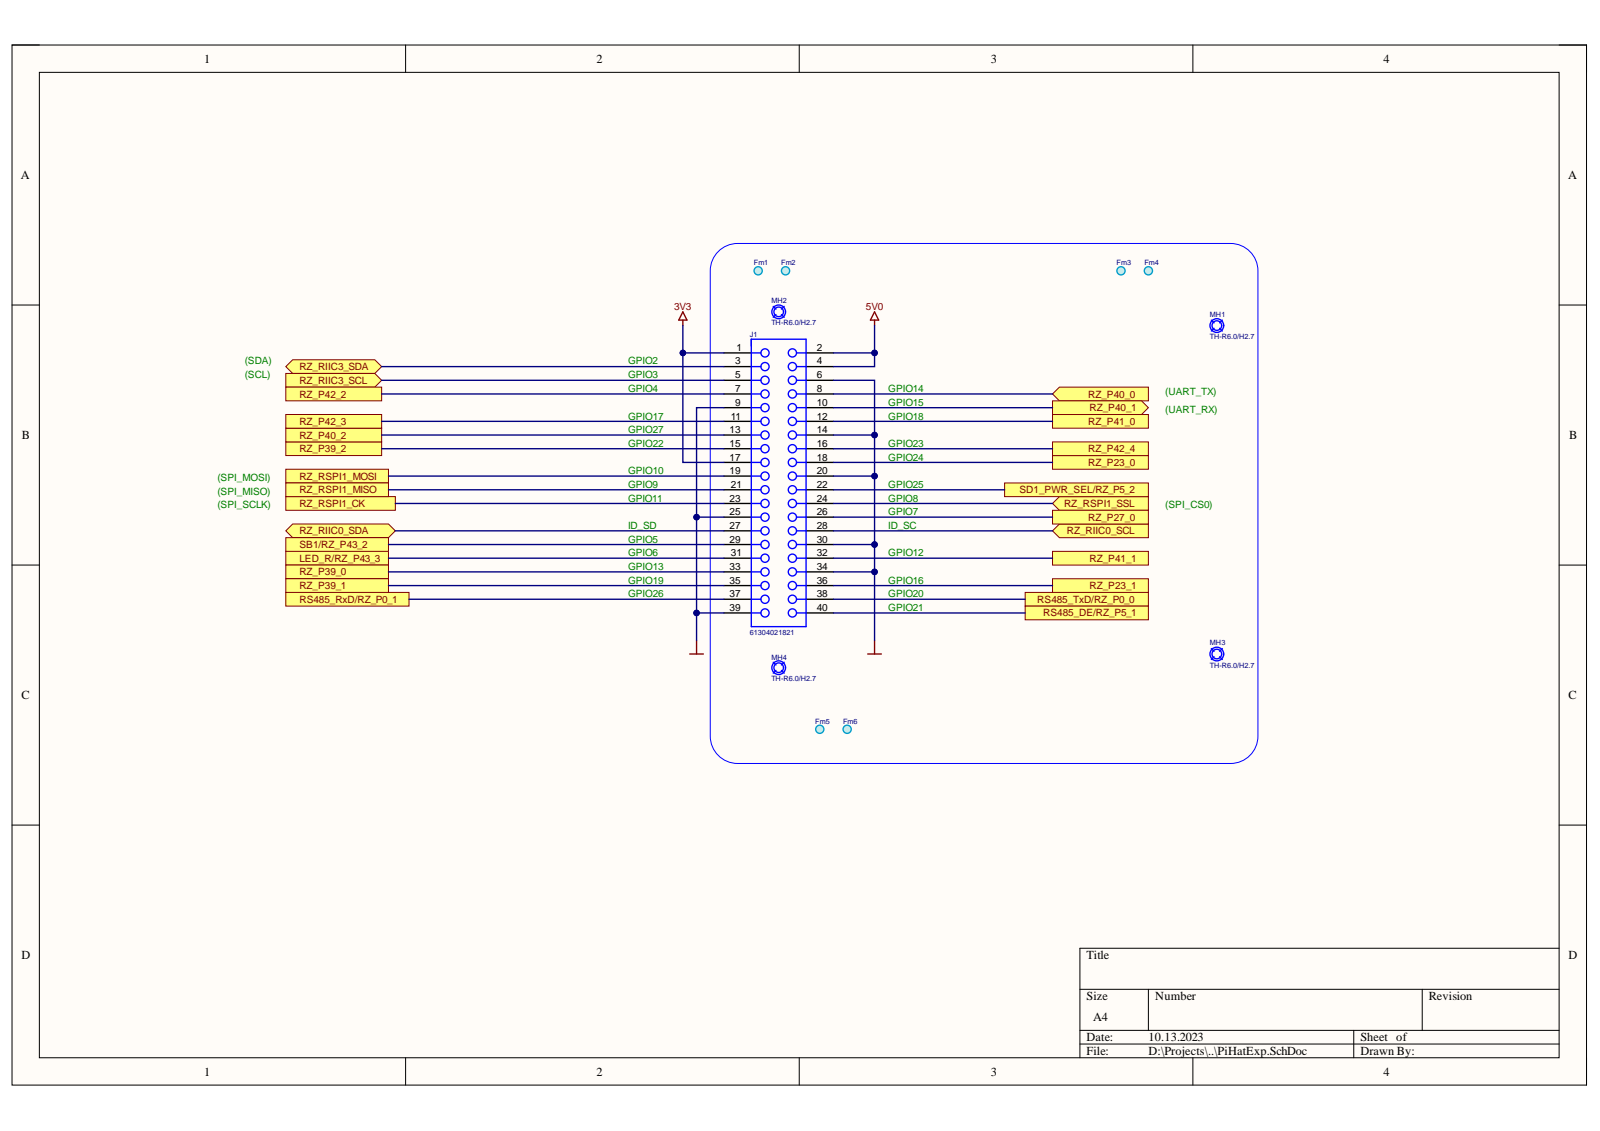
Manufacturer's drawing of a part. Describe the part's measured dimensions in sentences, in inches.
The part is named "PCB; Board; J1; 61304021821 (+1 more)". Its 3-D file was written by "Open CASCADE 7.5 (AUTOMOTIVE_DESIGN)". It is 42 solids with 1559 faces: 1344 planar, 135 cylindrical and 80 other. Overall it measures 2.567 by 2.213 by 0.453 inches. Its volume is 0.448 cubic inches and its surface area 18.71 square inches. Round holes: 40 of diameter 0.04, 4 of diameter 0.106. Partial cylindrical surfaces (rounded edges, fillets, slot ends): 40 of radius 0.023, 3 of radius 0.122, 1 of radius 0.022, 1 of radius 0.031, 1 of radius 0.035, 1 of radius 0.122. The main face-to-face distances are 0.063, 0.1, 0.022, 0.036, 0.064, 0.136, 0.164, 0.028, 0.2, 0.016. The hole center spacings are 0.1, 0.2, 0.141, 0.3, 0.224, 0.4, 0.316, 0.5.
